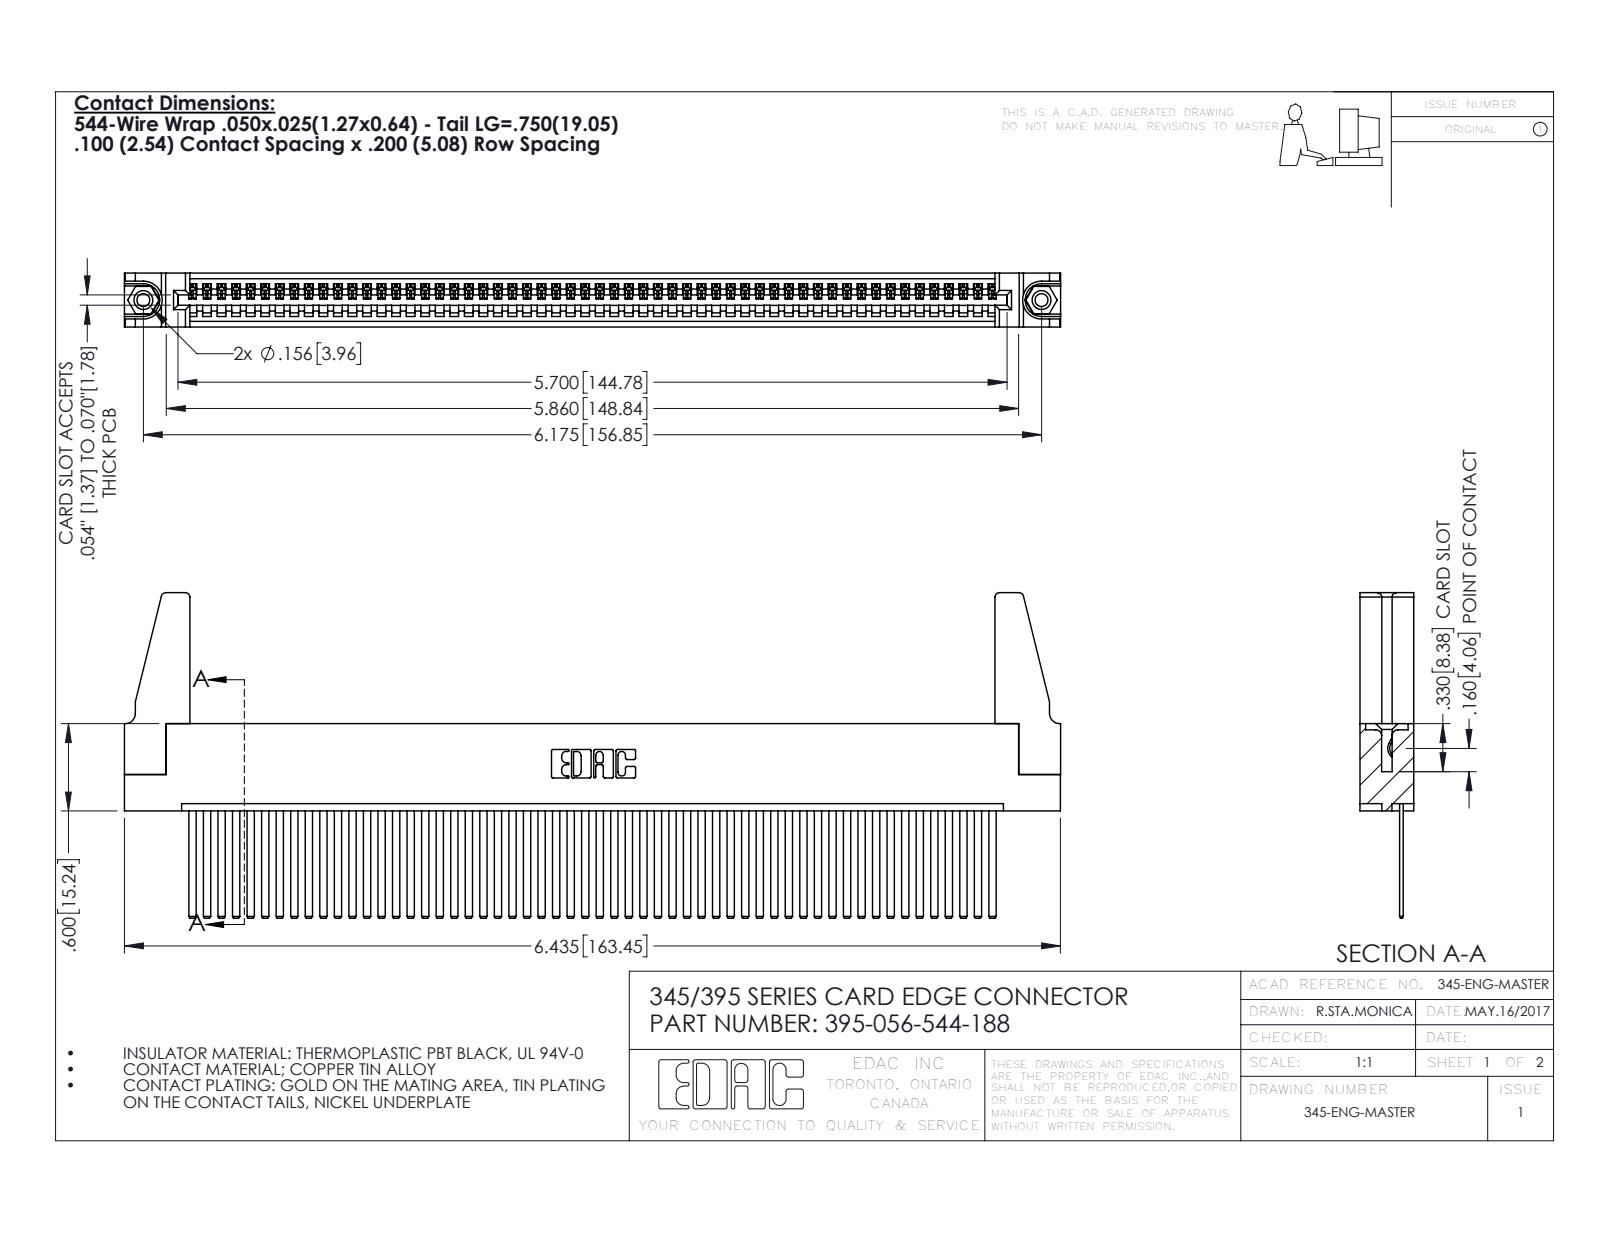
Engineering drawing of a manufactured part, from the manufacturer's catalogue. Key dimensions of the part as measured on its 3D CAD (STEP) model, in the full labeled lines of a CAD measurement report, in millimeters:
Part name (STEP PRODUCT): 345-292-001_345-293-144; 345 Part_Flush Mounting Lugs - 0.156 Dia-TH; 345-250-001_345-250-001-102; 345-220-078_345-220-088 (+1 more)
STEP written by: SolidWorks 2016 (CONFIG_CONTROL_DESIGN)
Units: millimetres
Bodies: 61 solids, 3162 faces (2168 planar, 978 cylindrical, 16 other)
Overall size (bounding box): 163.5 × 56.8 × 9.4
Volume: 19 550 mm³ · Surface area: 26 920 mm²
Round holes (diameter × count): ⌀2.3 ×2, ⌀3.2 ×2, ⌀4 ×2, ⌀1.6 ×1
Round bosses / shafts (diameter × count): ⌀3.9 ×2
Partial cylindrical surfaces — rounded edges, fillets, slot ends (radius × count): R0.2 ×112, R0.3 ×22, R0.8 ×8, R0.2 ×6, R0.8 ×6, R0.7 ×3, R0.8 ×2, R1 ×2
Main face-to-face distances: 1.8, 7.6, 2.5, 6.9, 0.6, 9.4, 5.1, 5.7, 3.8, 1.8
Hole centre spacings: 6.9, 150.9, 156.8
